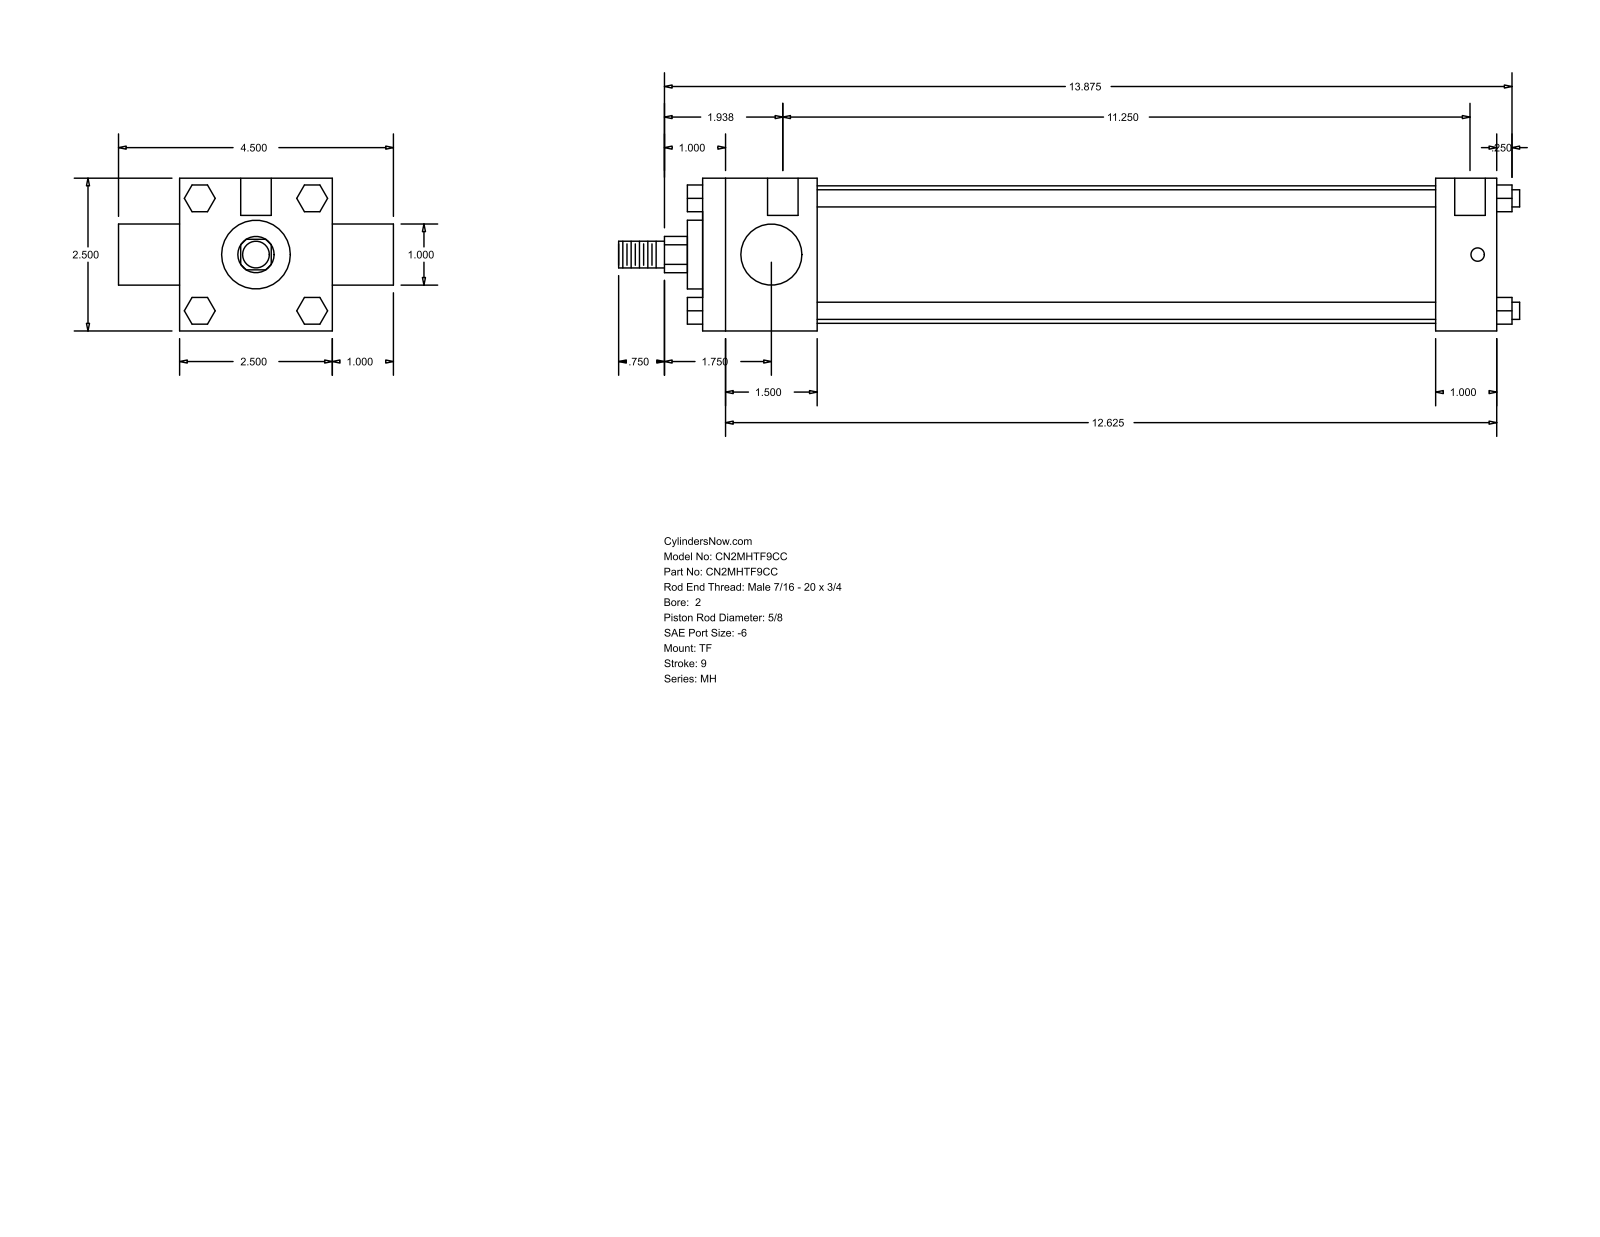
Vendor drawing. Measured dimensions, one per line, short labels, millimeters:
name: MH_TF__0200_0.625
written by: GSSL Pune (CONFIG_CONTROL_DESIGN)
unit: mm
bodies: 0 solids, 120 faces (92 planar, 28 cylindrical, 0 other)
size: 374.65 × 114.3 × 63.5
holes: 3× ⌀5.56, 2× ⌀12.7
bosses: 4× ⌀7.14, 1× ⌀57.15, 1× ⌀28.57, 1× ⌀25.4, 1× ⌀15.88, 1× ⌀11.11
rounds: 1× R7.54
face distances: 63.5, 330.19, 47.62, 304.8, 257.18, 282.57, 25.39, 25.4, 88.9, 6.35
hole spacings: 3.18, 4.76, 285.75, 288.93, 290.51, 293.69
